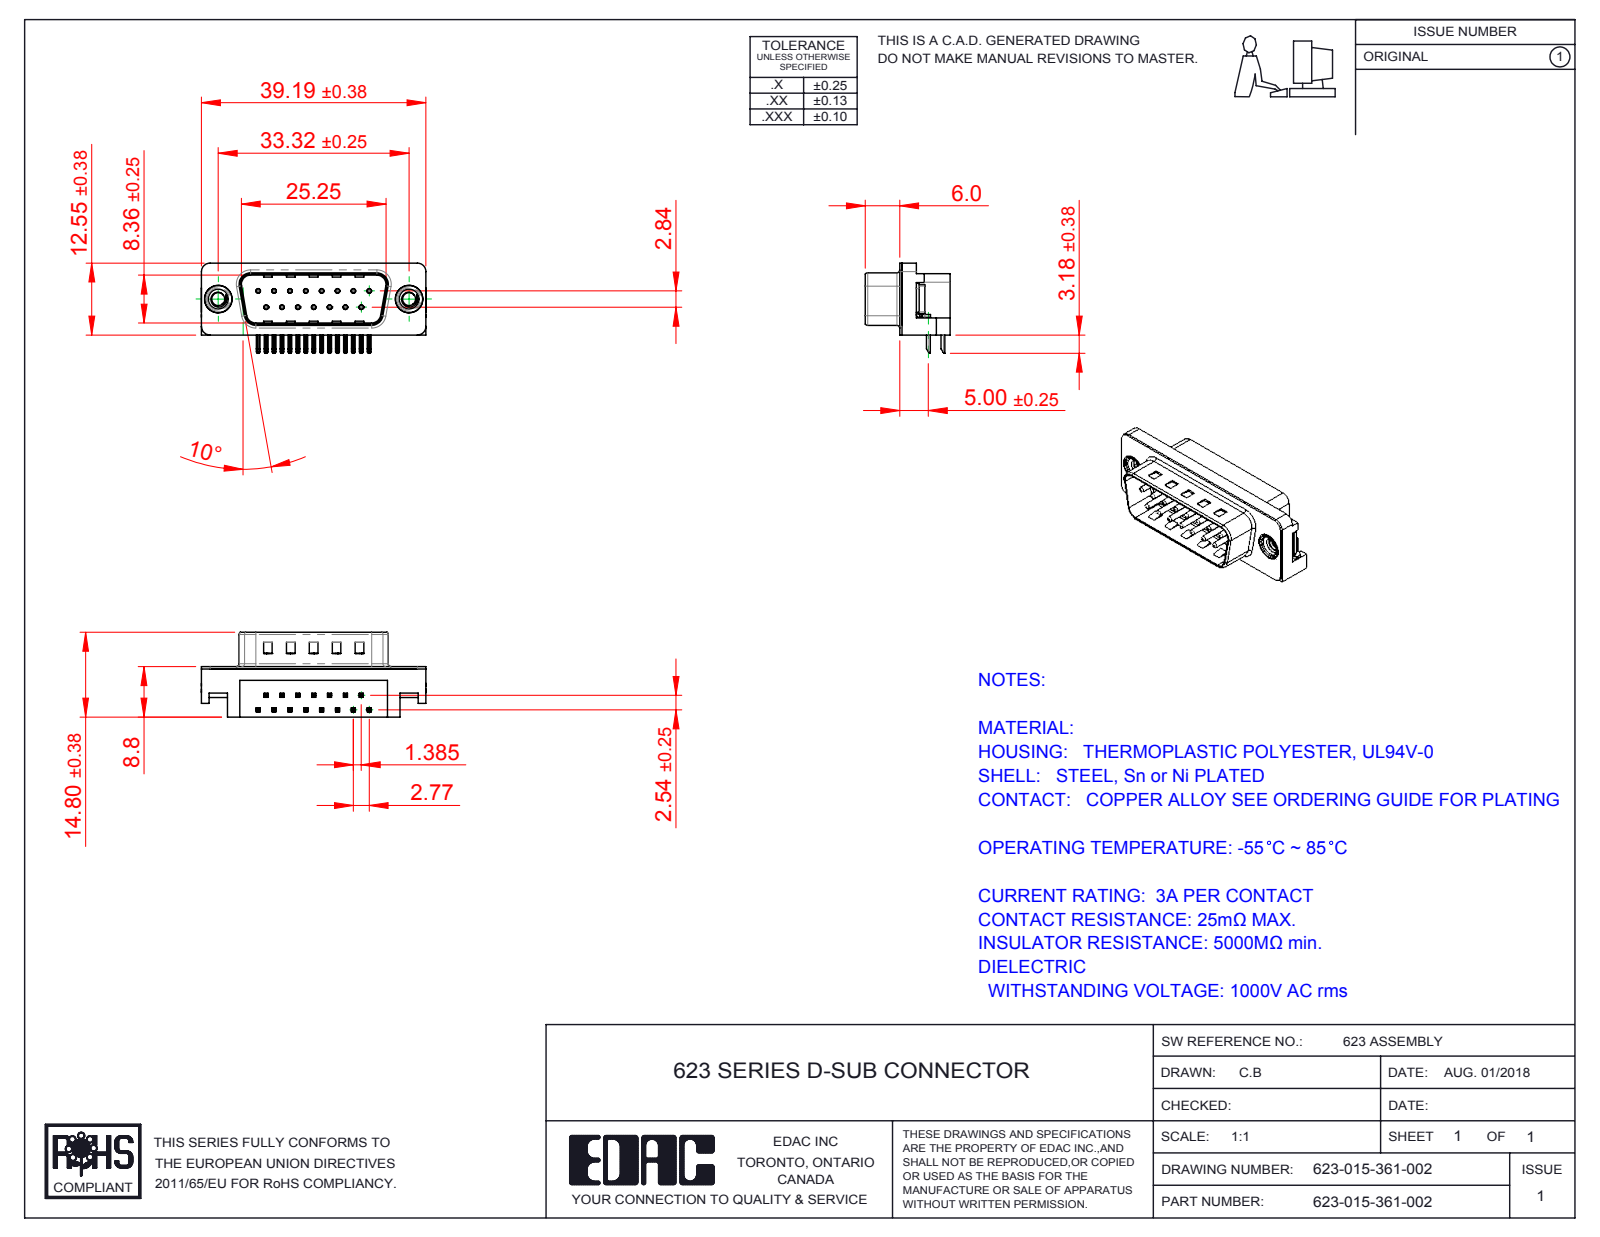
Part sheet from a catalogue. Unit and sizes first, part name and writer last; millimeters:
Units: millimetres
Overall size (bounding box): 39.22 × 15.73 × 14.8
Round holes (diameter × count): ⌀0.35 ×15, ⌀0.8 ×15, ⌀2.26 ×2, ⌀4 ×2, ⌀4.8 ×2, ⌀5 ×2
Round bosses / shafts (diameter × count): ⌀0.75 ×15, ⌀4.9 ×2, ⌀4.75 ×2, ⌀3.9 ×2
Partial cylindrical surfaces — rounded edges, fillets, slot ends (radius × count): R0.25 ×68, R0.12 ×30, R1 ×16, R0.5 ×9, R1.5 ×6, R0.9 ×4, R1.6 ×4, R2 ×4
Main face-to-face distances: 0.4, 8.4, 2.1, 1.7, 10.46, 8.8, 10.86, 8.76, 5.9, 2.9
Hole centre spacings: 3.16, 2.77, 5.54, 8.31, 11.08, 5.03, 5.04, 7.48
Volume: 3 319 mm³ · Surface area: 4 885 mm²
Bodies: 21 solids, 1467 faces (893 planar, 435 cylindrical, 139 other)
Part name (STEP PRODUCT): 623 Non Board Mount; 623-015-361-002; 623 4-40 Threaded Rivet; 623 Contact Top (+3 more)
STEP written by: SolidWorks 2016 (CONFIG_CONTROL_DESIGN)
